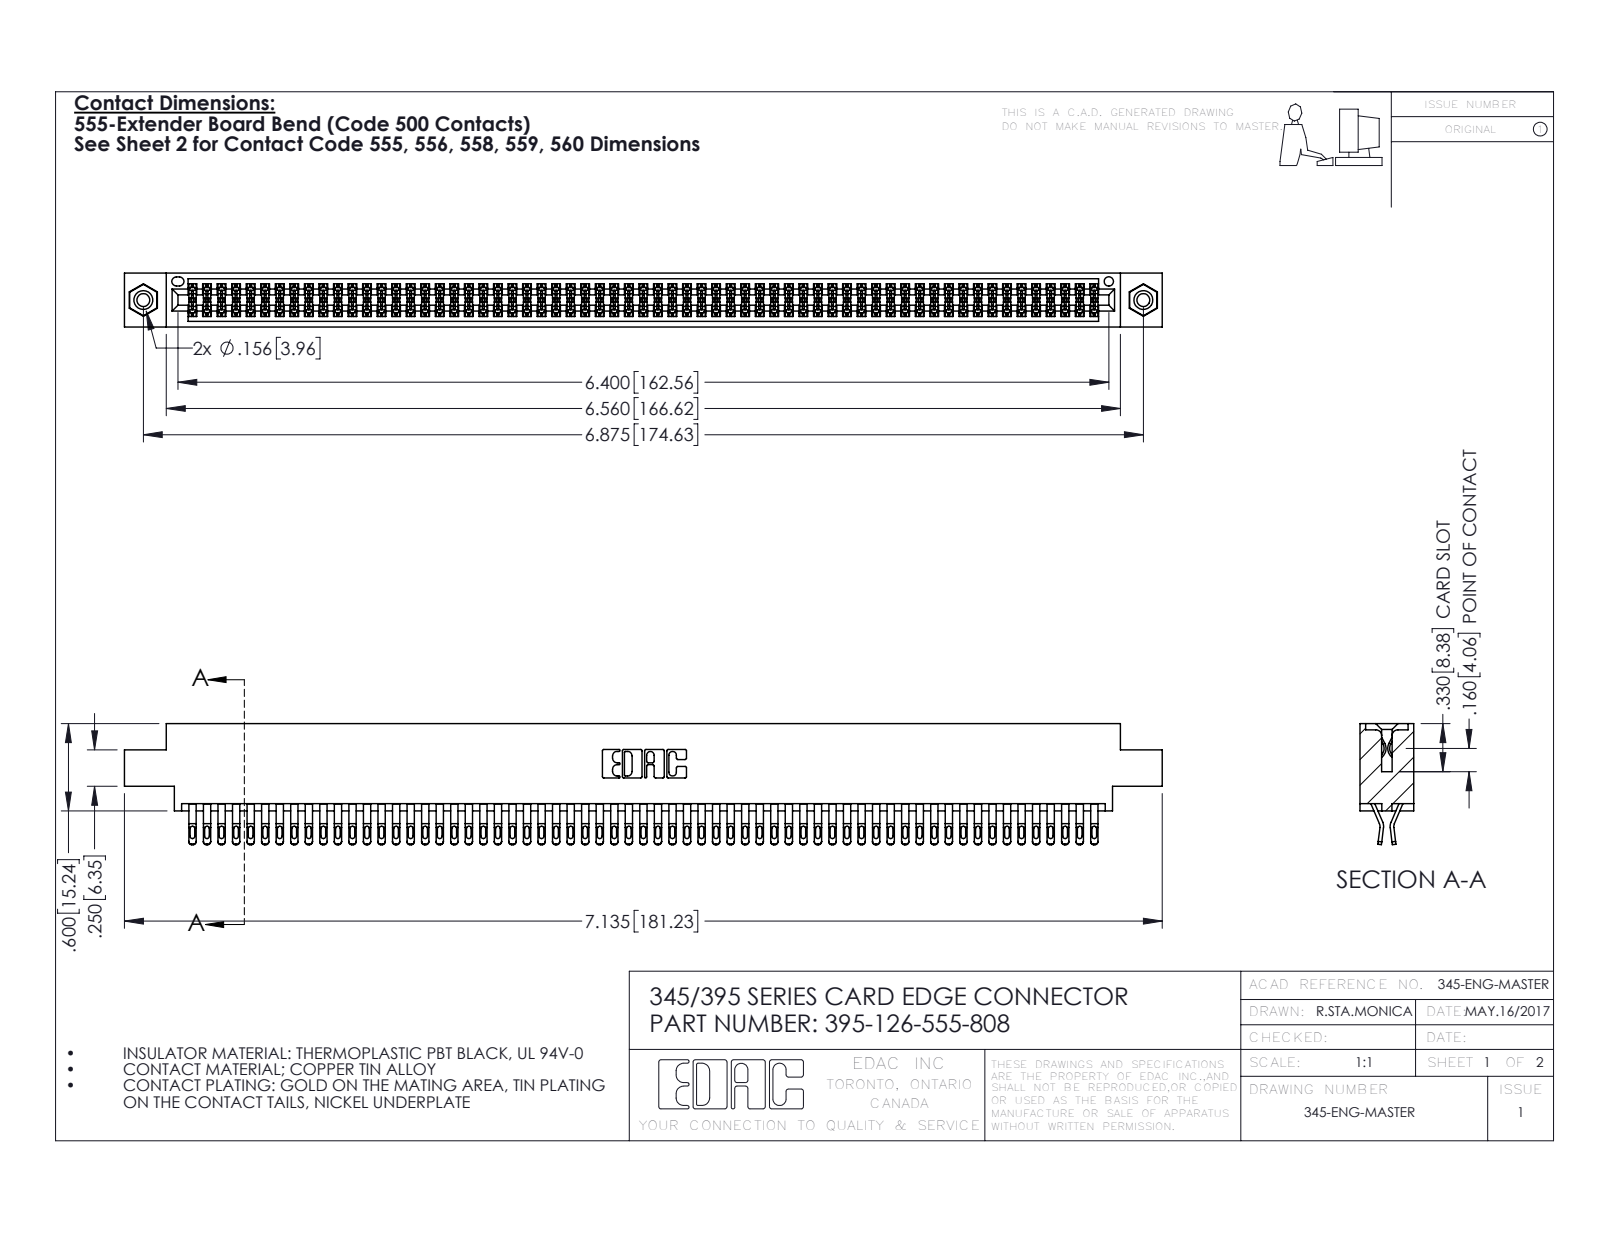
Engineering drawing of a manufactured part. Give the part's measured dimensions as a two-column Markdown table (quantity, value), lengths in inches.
| quantity | value |
| --- | --- |
| part name | 345 Part_0.170 Offset - 0.156 Dia-TI; 395-126-555-808; 345-250-001_345-250-003-102; 345-292-001_555 Tail |
| STEP written by | SolidWorks 2016 (CONFIG_CONTROL_DESIGN) |
| units | inches |
| bodies | 129 solids, 7246 faces (4022 planar, 3208 cylindrical, 16 other) |
| overall size | 7.135 × 0.832 × 0.37 |
| volume | 1.101 in³ |
| surface area | 44.19 in² |
| round holes (diameter × count) | 0.089 × 2, 0.125 × 2, 0.156 × 2, 0.064 × 1 |
| round bosses / shafts (diameter × count) | 0.155 × 2 |
| partial cylindrical surfaces (radius × count) | 0.016 × 315, 0.02 × 252, 0.006 × 189, 0.01 × 22, 0.007 × 6, 0.031 × 6, 0.026 × 3, 0.01 × 2 |
| main face-to-face distances | 0.072, 0.298, 0.025, 0.37, 0.2, 0.098, 0.272, 0.225, 0.175, 0.149 |
| hole center spacings | 0.27, 6.639, 6.875 |
